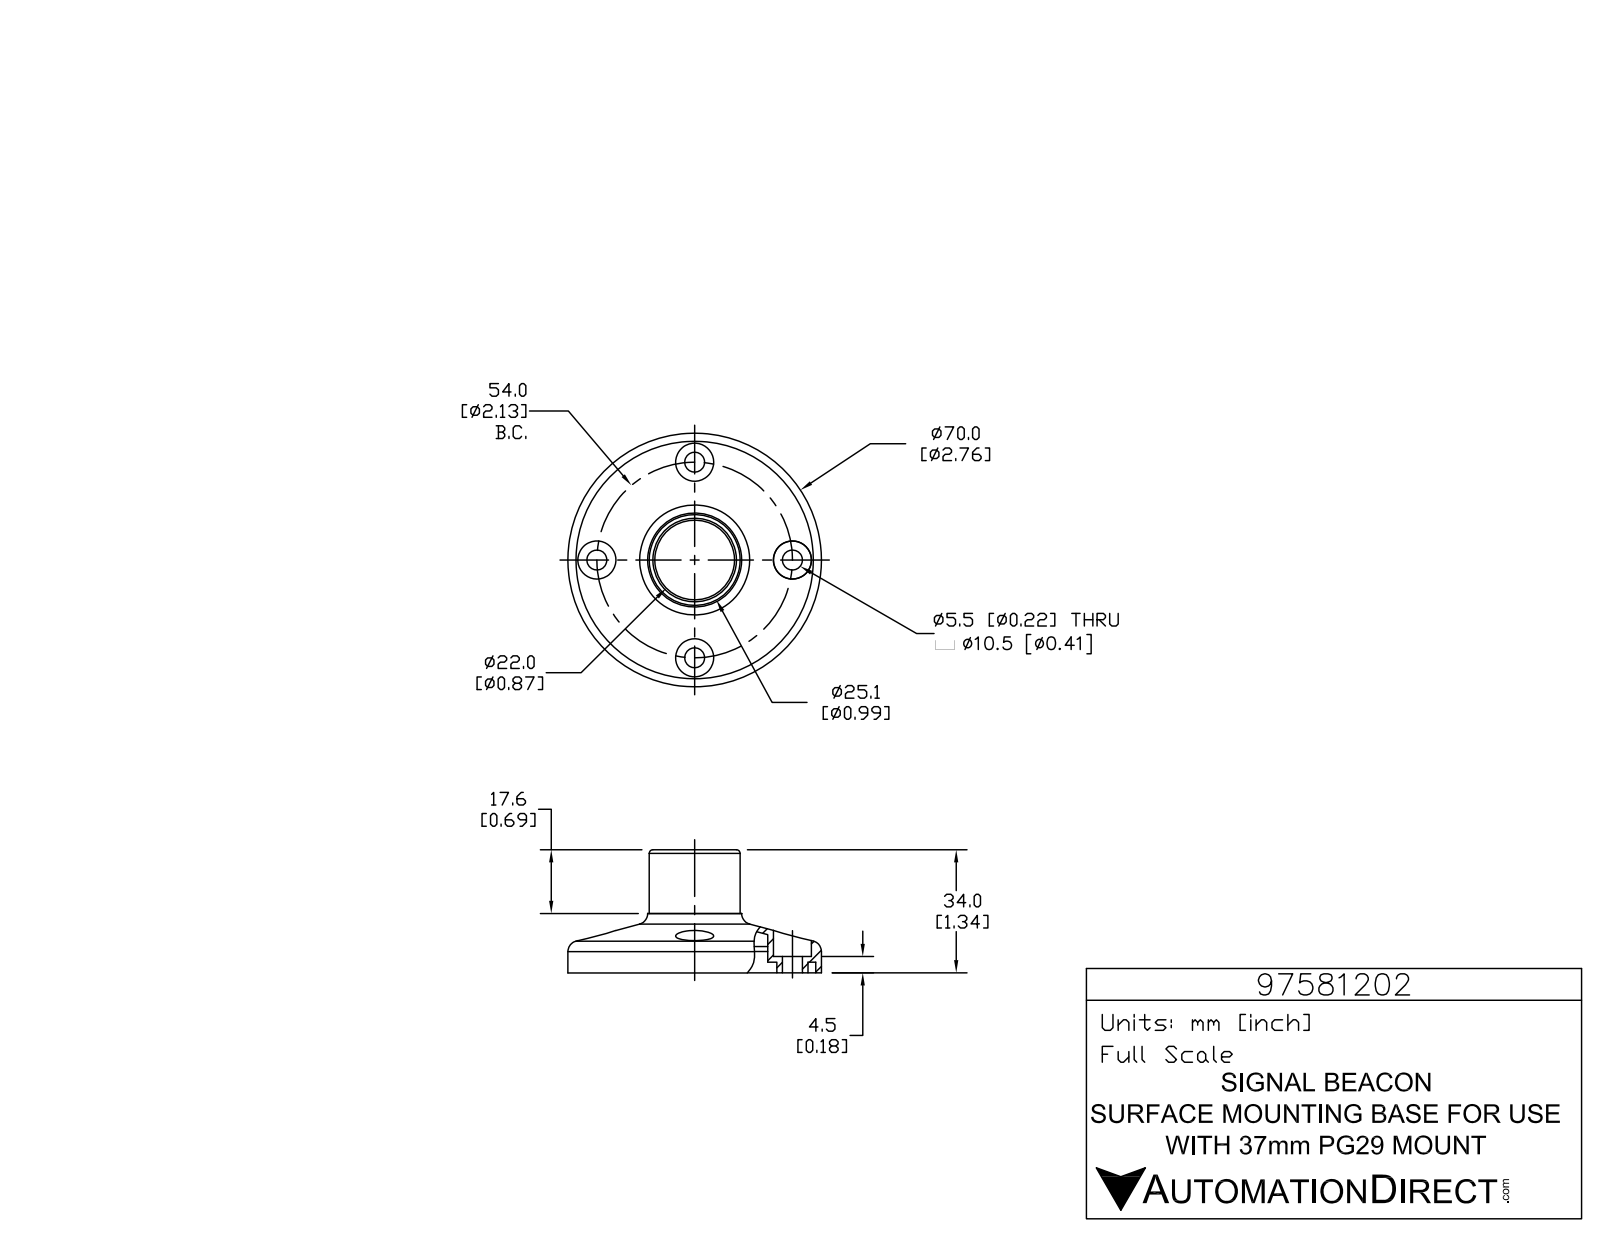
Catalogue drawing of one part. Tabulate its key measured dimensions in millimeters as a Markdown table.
| quantity | value |
| --- | --- |
| part name | 97581202 |
| STEP written by | SolidWorks 2017 (AUTOMOTIVE_DESIGN) |
| units | millimeters |
| bodies | 1 solid, 810 faces (531 planar, 269 cylindrical, 10 other) |
| overall size | 70.1 × 70.1 × 35.5 |
| volume | 45 720 mm³ |
| surface area | 14 340 mm² |
| round holes (diameter × count) | 5.5 × 4, 6 × 4, 10.5 × 4, 1 × 3, 19 × 1, 40 × 1 |
| round bosses / shafts (diameter × count) | 5.7 × 3, 1.4 × 3, 70 × 1, 25.1 × 1 |
| partial cylindrical surfaces (radius × count) | 0.2 × 6, 0.2 × 6, 0.2 × 6, 3.3 × 6, 0.1 × 3, 0.1 × 3, 0.2 × 3, 0.2 × 3 |
| main face-to-face distances | 1.5, 4.5, 6, 29.5, 34, 35.5, 17.6, 11.9, 16.4, 17.9 |
| hole center spacings | 27, 38.2, 54 |
